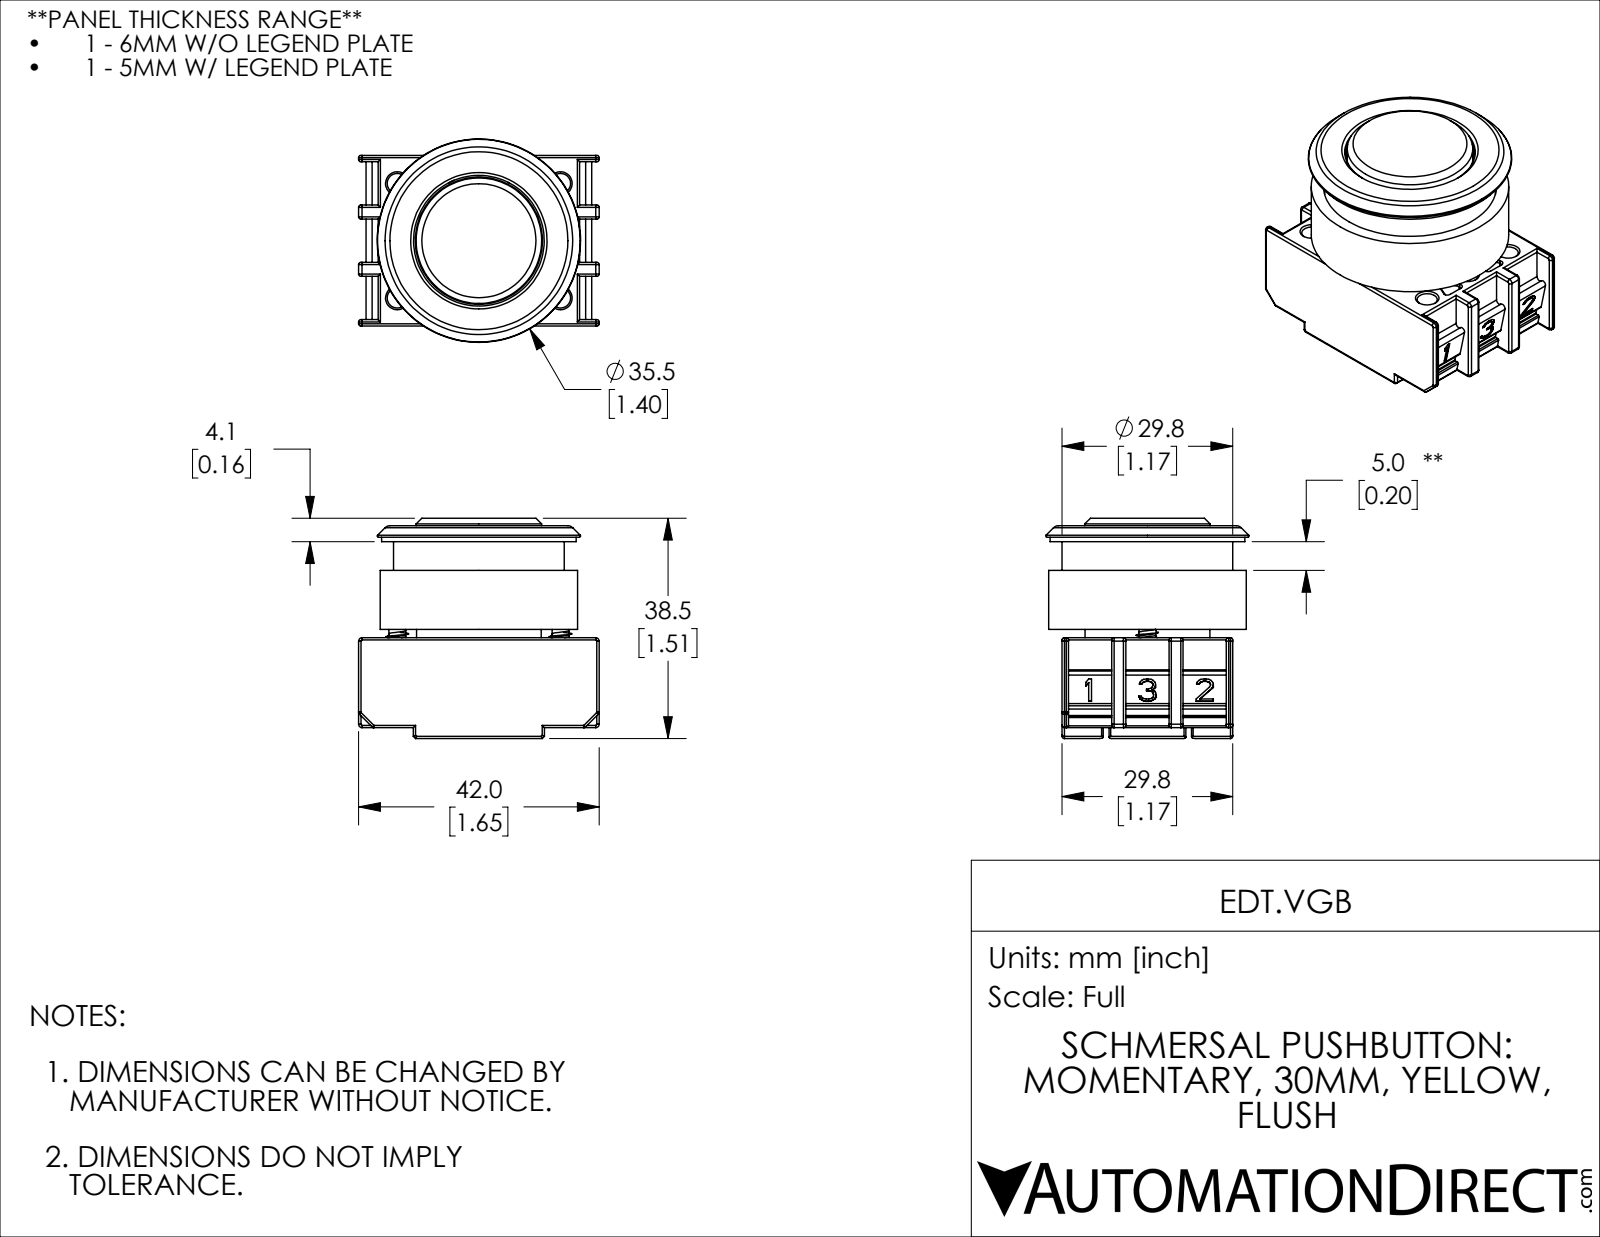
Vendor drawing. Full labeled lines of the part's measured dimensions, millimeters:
Part name (STEP PRODUCT): EDT.VGB
STEP written by: SolidWorks 2019 (CONFIG_CONTROL_DESIGN)
Units: millimetres
Bodies: 3 solids, 1361 faces (509 planar, 460 cylindrical, 392 other)
Overall size (bounding box): 42 × 38.45 × 35.5
Volume: 22 602 mm³ · Surface area: 20 491 mm²
Round holes (diameter × count): ⌀3.5 ×6, ⌀5.15 ×6, ⌀4.1 ×1, ⌀12.5 ×1, ⌀18 ×1, ⌀19.2 ×1, ⌀22.2 ×1, ⌀22.8 ×1, ⌀24.2 ×1, ⌀26 ×1, ⌀27 ×1, ⌀30.2 ×1
Round bosses / shafts (diameter × count): ⌀4.8 ×2, ⌀2.93 ×2, ⌀34.5 ×1, ⌀34 ×1, ⌀29.8 ×1, ⌀24.6 ×1, ⌀21.9 ×1, ⌀21.8 ×1
Partial cylindrical surfaces — rounded edges, fillets, slot ends (radius × count): R0.4 ×112, R0.3 ×48, R0.2 ×24, R0.6 ×8, R0.5 ×6, R0.1 ×2, R0.6 ×2, R0.8 ×2
Main face-to-face distances: 29.8, 1.9, 19.4, 5.9, 4.1, 1.45, 16.2, 19.05, 10, 1.3
Hole centre spacings: 10, 17.41, 30.2, 28.5, 14.25, 20, 34.82
